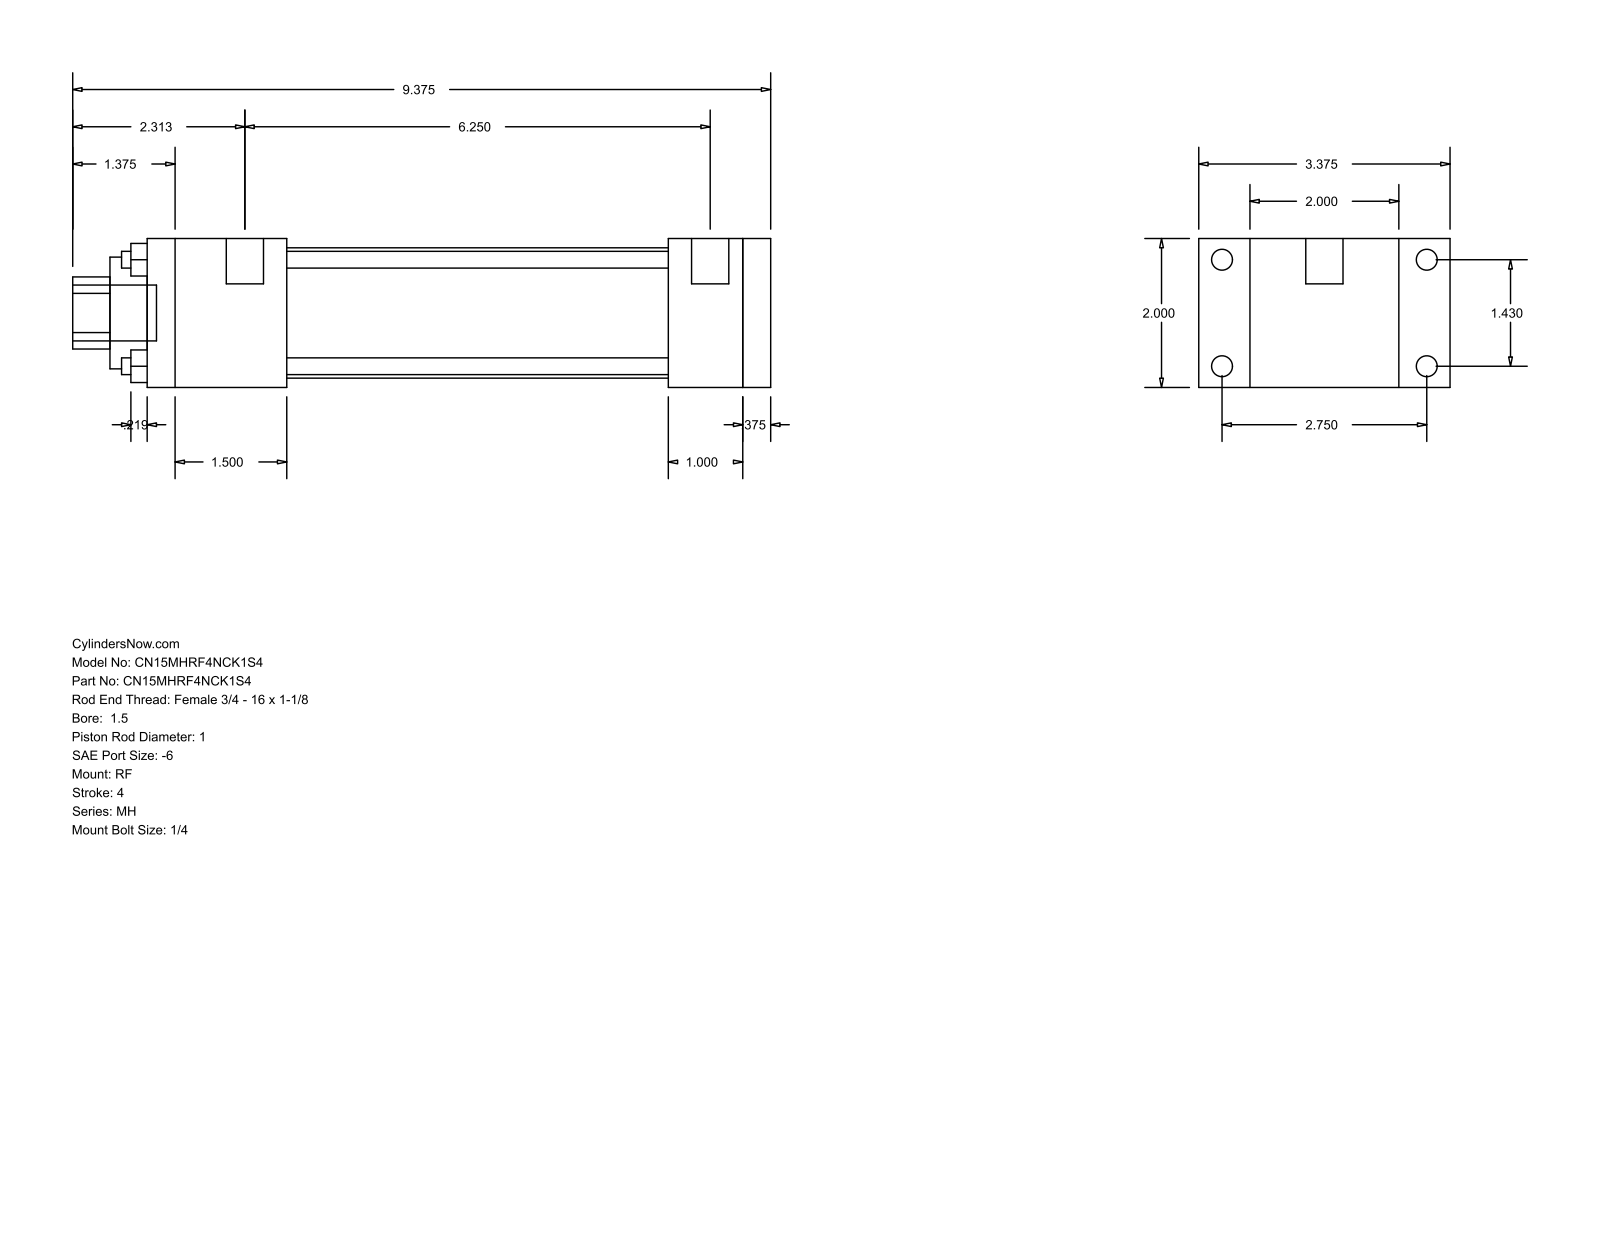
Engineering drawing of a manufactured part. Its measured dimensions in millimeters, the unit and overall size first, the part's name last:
Units: millimetres
Overall size (bounding box): 238.12 × 85.72 × 50.8
Round holes (diameter × count): ⌀5.71 ×4, ⌀25.4 ×1, ⌀38.1 ×1, ⌀44.45 ×1
Round bosses / shafts (diameter × count): ⌀7.14 ×4, ⌀5.56 ×4, ⌀12.7 ×2, ⌀19.05 ×1
Partial cylindrical surfaces — rounded edges, fillets, slot ends (radius × count): R12.29 ×1
Main face-to-face distances: 50.8, 9.52, 203.2, 25.4, 212.72, 17.46, 68.26, 177.8, 34.92, 47.63
Hole centre spacings: 25.68, 36.32, 51.36
Bodies: 0 solids, 92 faces (64 planar, 28 cylindrical, 0 other)
Part name (STEP PRODUCT): MH_RF__0150_1
STEP written by: GSSL Pune (CONFIG_CONTROL_DESIGN)
